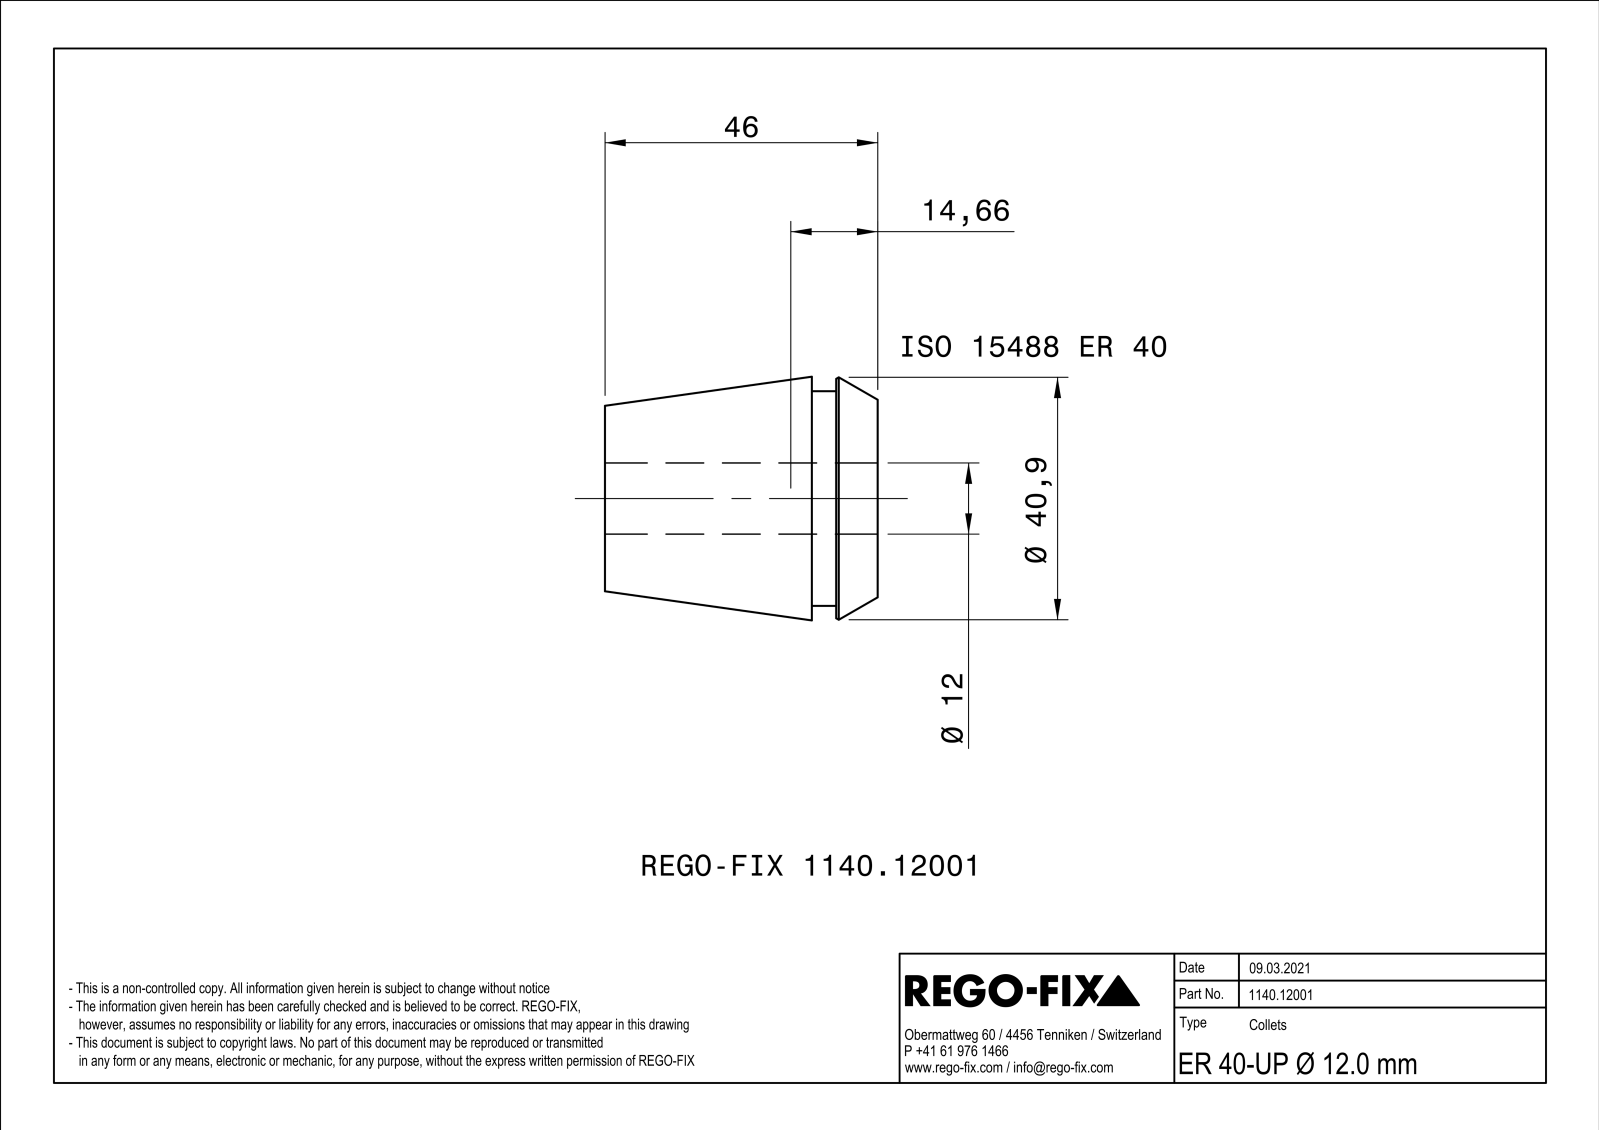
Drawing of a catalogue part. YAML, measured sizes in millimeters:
part_name: "NOCUT"
step_written_by: "SIEMENS PLM Software Solid Edge ST10 (AUTOMOTIVE_DESIGN)"
units: millimeters
bodies: {solids: 1, faces: 177, planar: 88, cylindrical: 9, other: 80}
overall_size: [46, 40.99, 40.99]
volume: 34724
surface_area: 23532
round_holes:
  - {diameter: 12, count: 1}
round_bosses_or_shafts:
  - {diameter: 36.2, count: 1}
face_to_face_distances: [1, 46, 11.1, 34.9, 7, 4.1, 39, 7.5, 0.5, 3.6]
